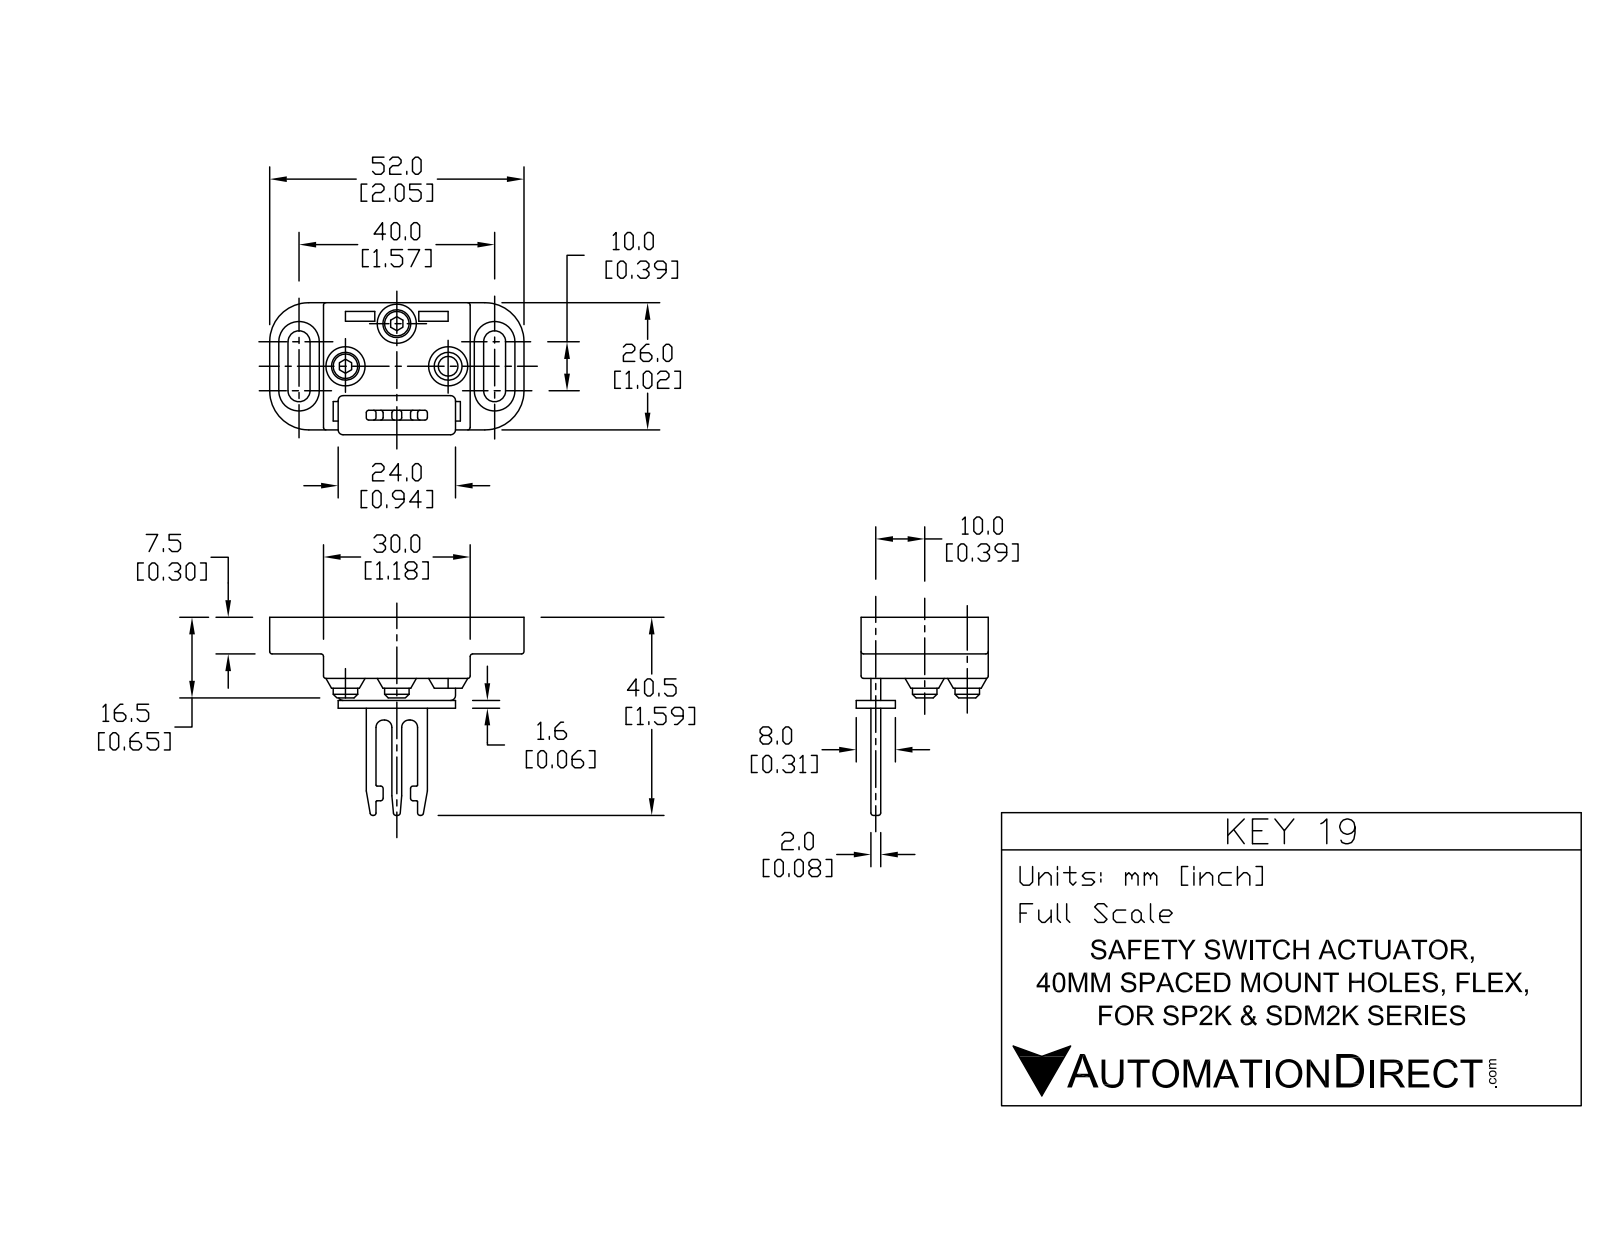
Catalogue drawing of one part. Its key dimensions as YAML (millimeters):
part_name: "KEY19"
step_written_by: "SolidWorks 2017 (AUTOMOTIVE_DESIGN)"
units: millimeters
bodies: {solids: 5, faces: 295, planar: 112, cylindrical: 127, other: 56}
overall_size: [52, 40.5, 26.8]
volume: 8900
surface_area: 9387
round_holes:
  - {diameter: 4, count: 3}
  - {diameter: 5, count: 3}
partial_cylinders:
  - {radius: 0.5, count: 54}
  - {radius: 1, count: 8}
  - {radius: 2.2, count: 6}
  - {radius: 0.2, count: 4}
  - {radius: 1.5, count: 4}
  - {radius: 2.3, count: 4}
  - {radius: 4.1, count: 4}
  - {radius: 8, count: 4}
face_to_face_distances: [2, 10.5, 8.5, 4, 26, 1.8, 24.2, 12.5, 6.5, 5]
hole_center_spacings: [13.6, 21]
